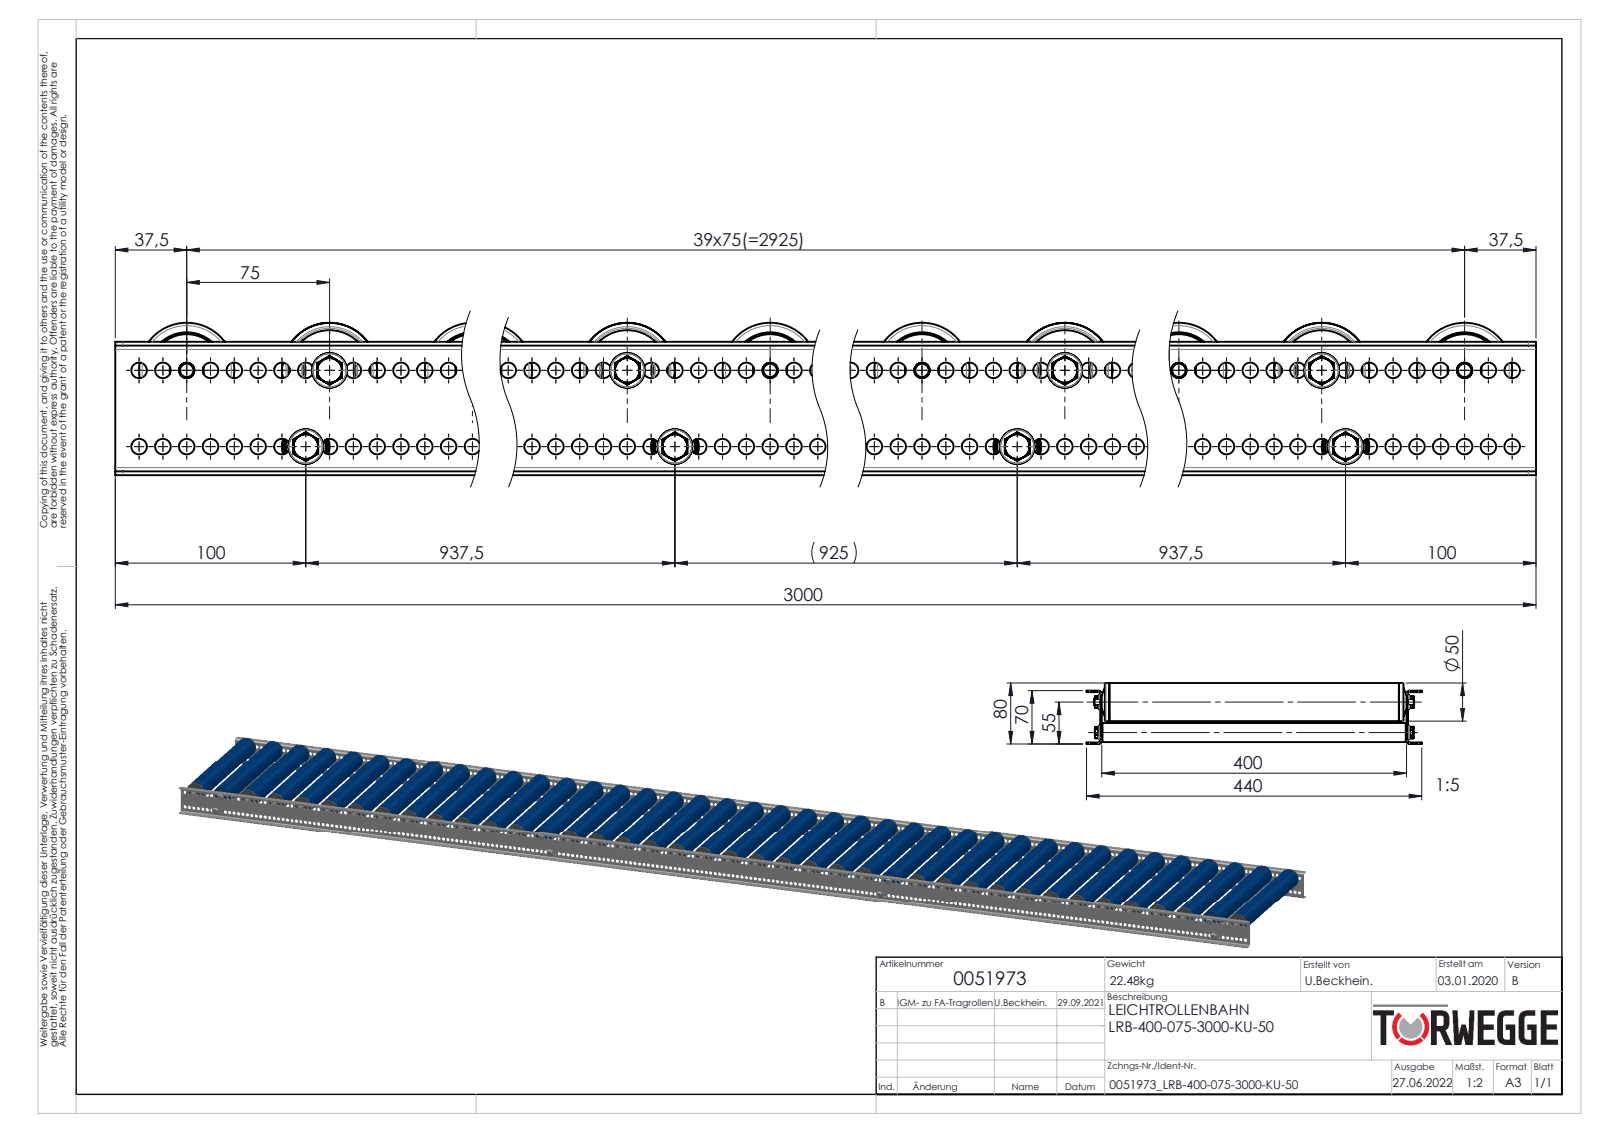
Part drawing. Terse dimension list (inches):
name: 0017015_Tragrollenrohr-Ø50x2,8KU_KFG_0017015_L=380; S100994_Sperrzahnschraube_M08x16-8.8-A2K; 0051973; Traversen_KFG_L400 (+8 more)
written by: SolidWorks 2020 (AUTOMOTIVE_DESIGN)
unit: in
bodies: 634 solids, 12220 faces (3052 planar, 5720 cylindrical, 3448 other)
size: 118.11 × 17.323 × 3.15
volume: 662.7 in³; area: 12 580 in²
holes: 478× ⌀0.323, 36× ⌀0.299, 36× ⌀0.315, 36× ⌀0.984, 36× ⌀1.181, 36× ⌀1.378, 36× ⌀1.551, 36× ⌀1.575, 8× ⌀0.268, 4× ⌀0.472, 4× ⌀0.476, 4× ⌀0.63
bosses: 40× ⌀1.969, 36× ⌀1.748, 36× ⌀1.496, 36× ⌀1.417, 36× ⌀1.299, 36× ⌀0.866, 36× ⌀0.827, 8× ⌀0.984
rounds: 72× R0.024, 72× R0.03, 72× R0.096, 36× R0.192, 36× R0.276, 8× R0.157, 4× R0.079, 4× R0.098
face distances: 0.079, 15.827, 2.677, 15.748, 15.906, 2.756, 2.598, 15.433, 0.472, 0.236
hole spacings: 0.492, 0.984, 1.476, 1.969, 2.461, 2.953, 3.445, 3.937
